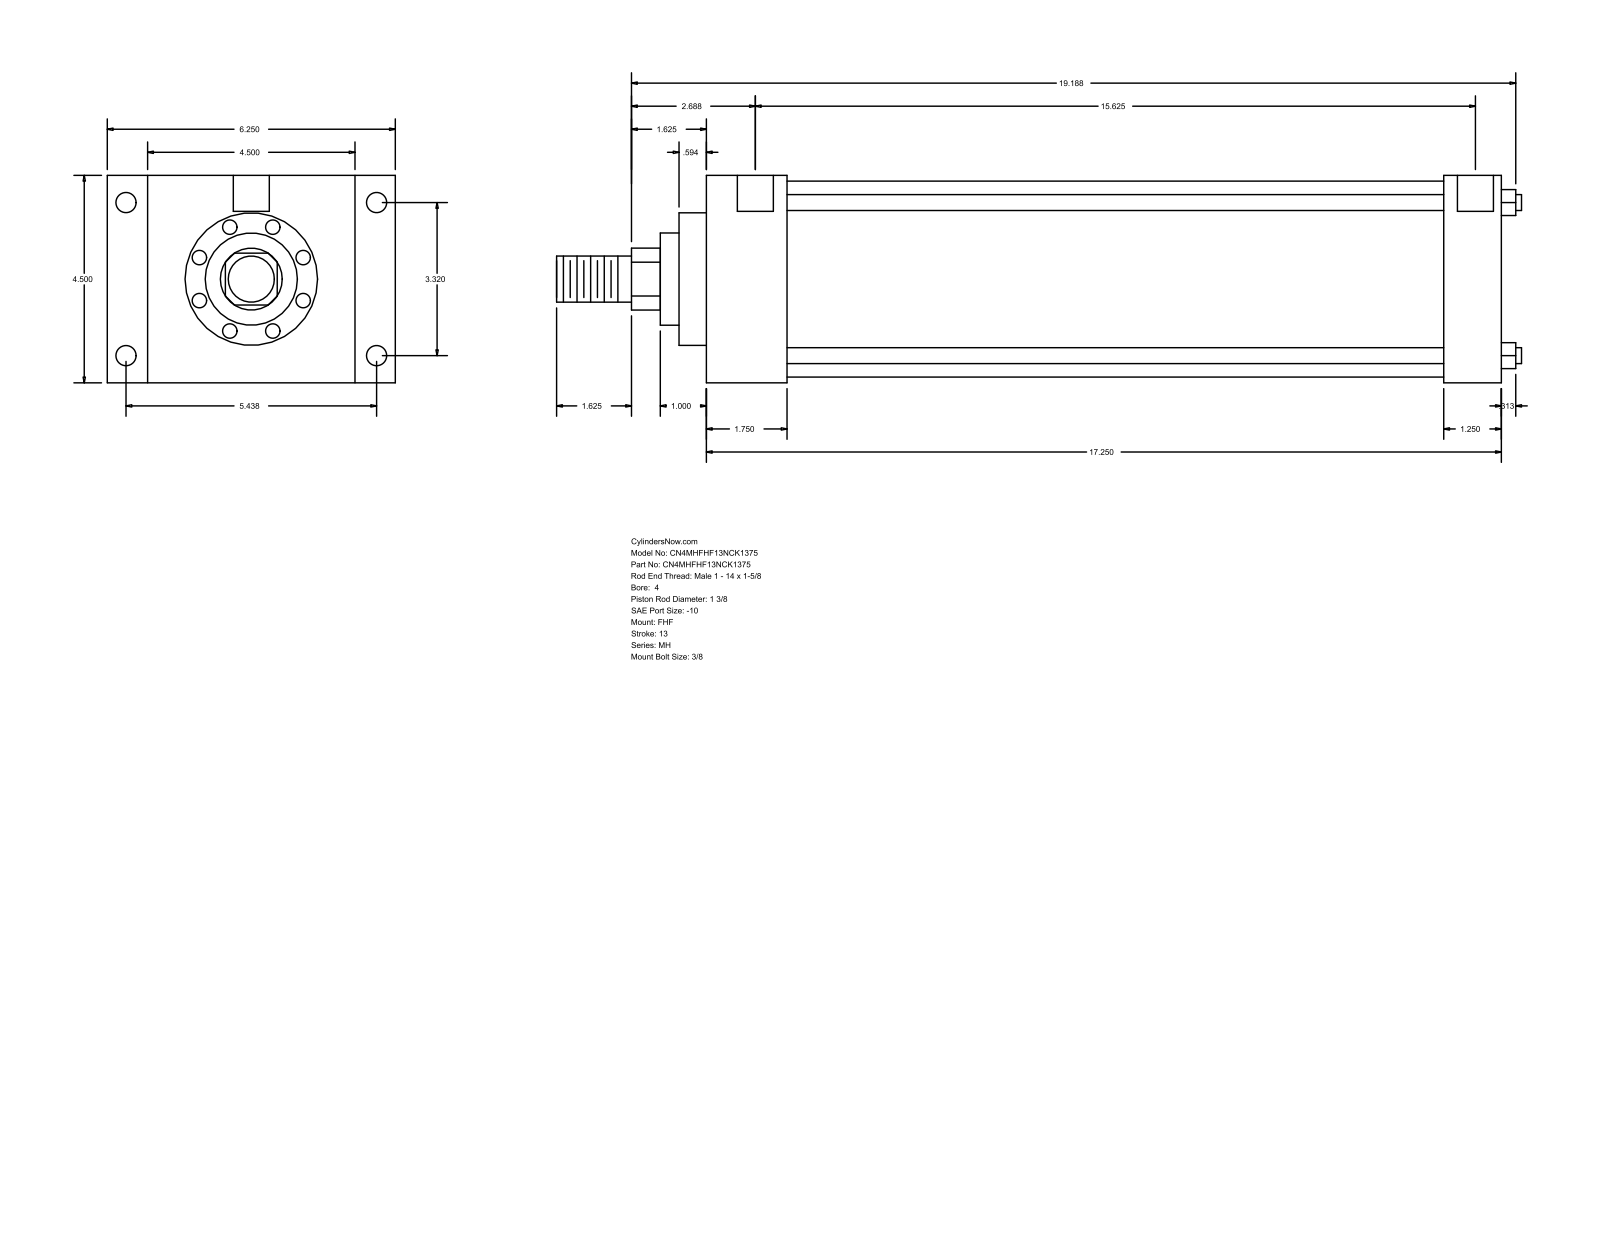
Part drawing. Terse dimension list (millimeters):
name: MH_FHF__0400_1.375
written by: GSSL Pune (CONFIG_CONTROL_DESIGN)
unit: mm
bodies: 0 solids, 90 faces (61 planar, 29 cylindrical, 0 other)
size: 531.81 × 158.75 × 114.3
holes: 4× ⌀8.73, 4× ⌀11.13, 2× ⌀19.84
bosses: 4× ⌀8.76, 1× ⌀107.95, 1× ⌀73.03, 1× ⌀50.8, 1× ⌀34.92, 1× ⌀25.4
rounds: 1× R17.06
face distances: 114.3, 438.16, 44.45, 393.71, 22.23, 136.53, 158.76, 406.41, 361.96, 31.75
hole spacings: 1.59, 84.32, 138.12, 161.82, 398.47, 400.06, 396.88
